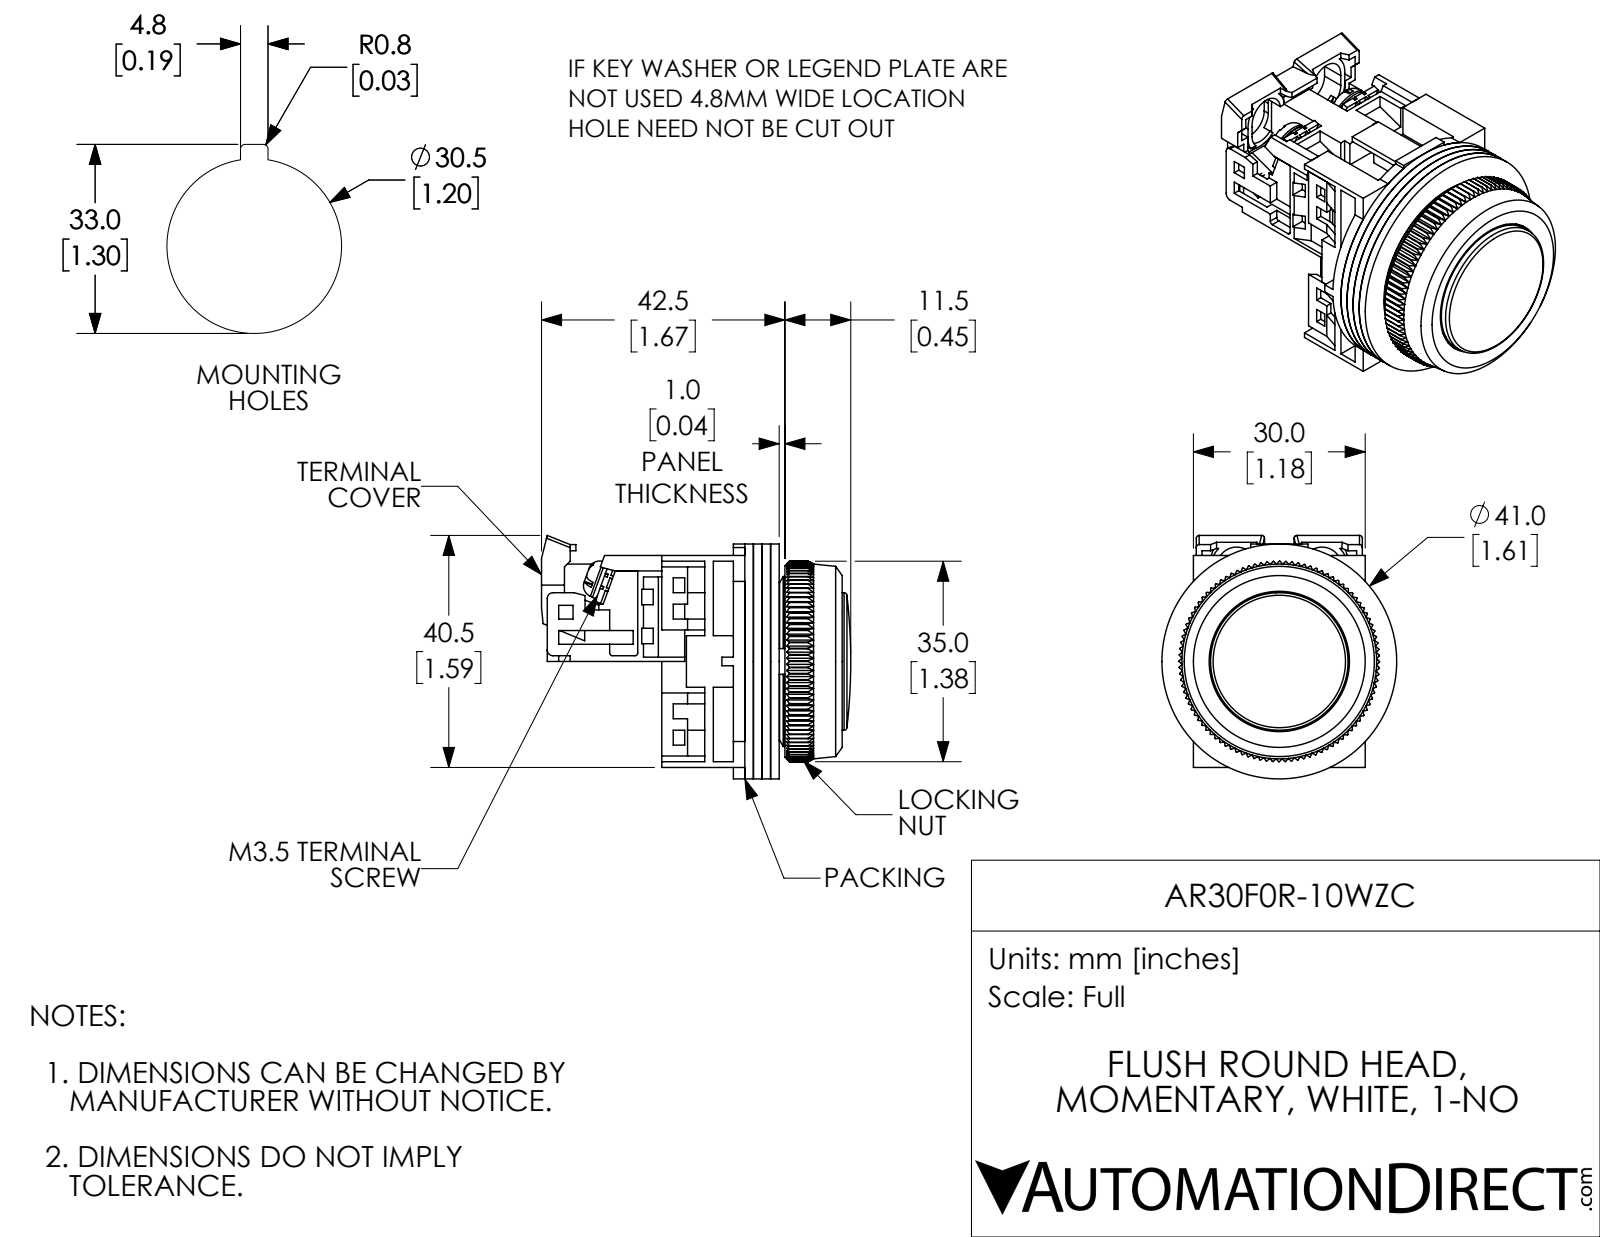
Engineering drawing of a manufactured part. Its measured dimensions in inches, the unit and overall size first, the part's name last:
Units: inches
Overall size (bounding box): 2.125 × 1.673 × 1.614
Round holes (diameter × count): ⌀0.138 ×4, ⌀0.142 ×2, ⌀0.118 ×1, ⌀0.472 ×1, ⌀0.709 ×1, ⌀0.787 ×1, ⌀0.827 ×1, ⌀0.945 ×1, ⌀0.965 ×1, ⌀1.122 ×1, ⌀1.252 ×1
Round bosses / shafts (diameter × count): ⌀0.26 ×2, ⌀0.138 ×2, ⌀1.614 ×1, ⌀1.181 ×1, ⌀0.906 ×1, ⌀0.866 ×1, ⌀0.551 ×1
Partial cylindrical surfaces — rounded edges, fillets, slot ends (radius × count): R0.059 ×8, R0.02 ×6, R0.039 ×2, R0.138 ×2, R0.177 ×2, R0.118 ×1, R0.398 ×1, R0.449 ×1
Main face-to-face distances: 0.059, 0.118, 0.177, 0.039, 0.197, 0.079, 0.689, 1.417, 0.256, 0.138
Hole centre spacings: 0.579, 0.61
Volume: 1.595 in³ · Surface area: 47.89 in²
Bodies: 16 solids, 1258 faces (798 planar, 249 cylindrical, 211 other)
Part name (STEP PRODUCT): AR30F0R-10WZC
STEP written by: SolidWorks 2017 (AUTOMOTIVE_DESIGN)
